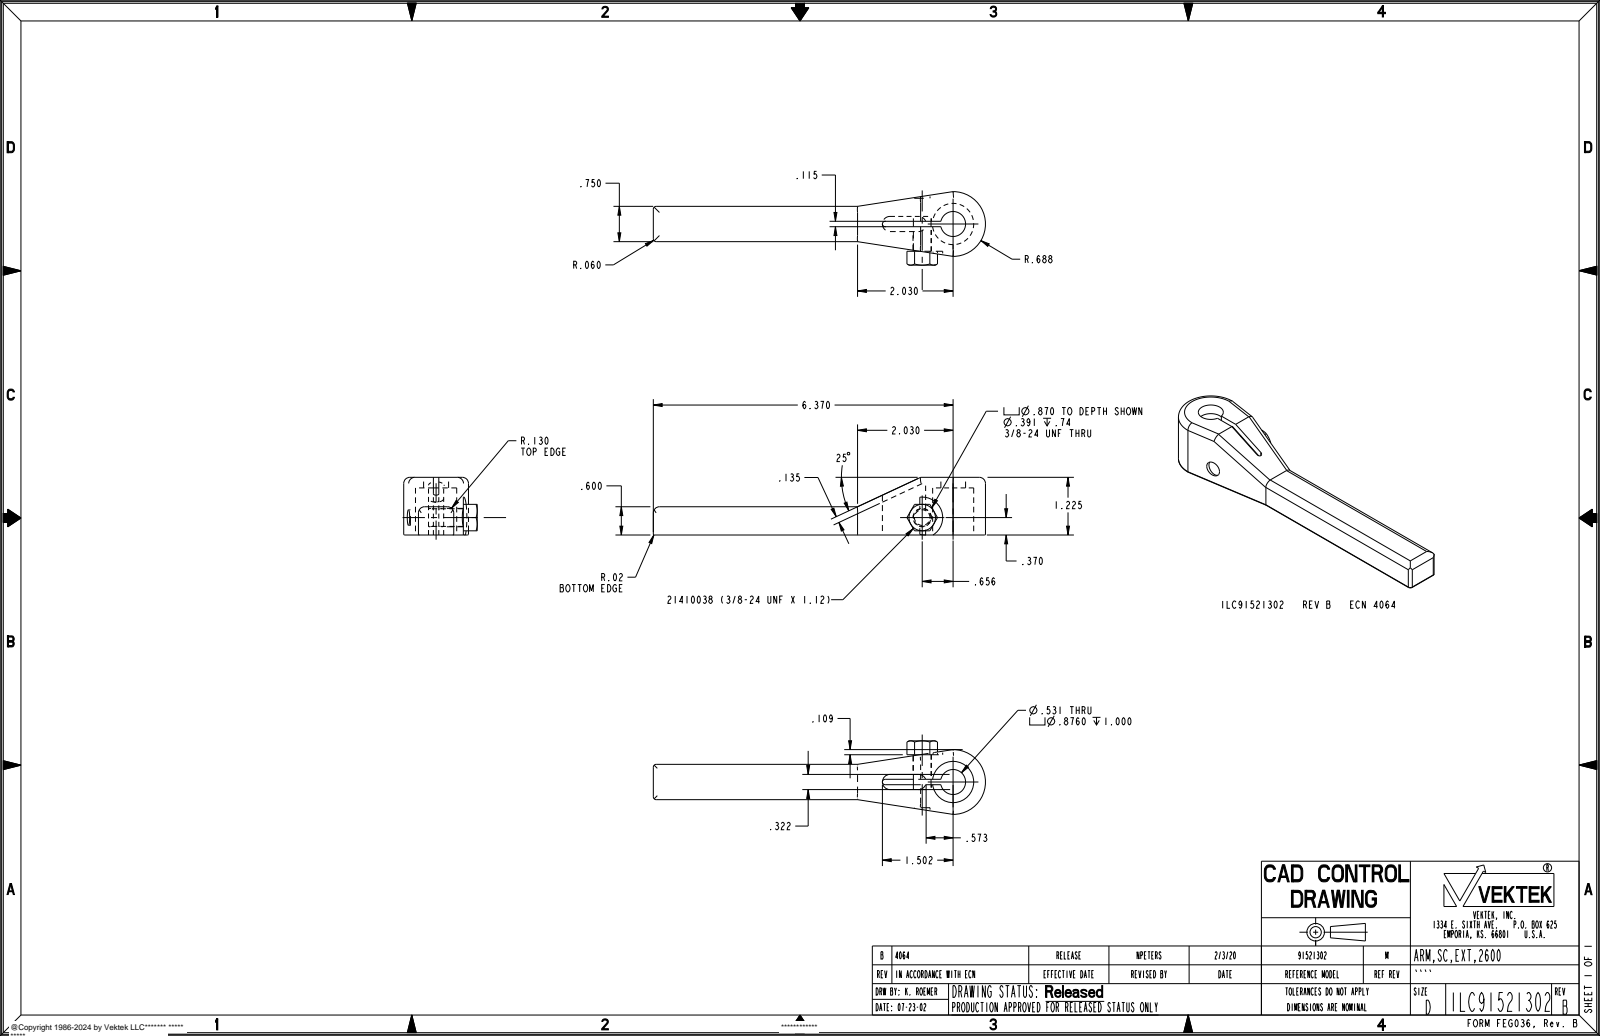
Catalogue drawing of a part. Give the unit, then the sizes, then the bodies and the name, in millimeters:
Units: millimetres
Overall size (bounding box): 179.3 × 39.7 × 31.1
Round holes (diameter × count): ⌀8.4 ×1, ⌀9.9 ×1, ⌀13.5 ×1, ⌀22.3 ×1
Round bosses / shafts (diameter × count): ⌀9.5 ×1
Partial cylindrical surfaces — rounded edges, fillets, slot ends (radius × count): R3.3 ×7, R0.5 ×5, R1.5 ×2, R4.1 ×2, R1.4 ×1, R11 ×1, R17.5 ×1
Main face-to-face distances: 15.2, 19.1, 5.4, 13.6, 31.1, 15.9, 8.1, 11, 2.6, 5.6
Volume: 69 170 mm³ · Surface area: 19 880 mm²
Bodies: 1 solid, 68 faces (26 planar, 32 cylindrical, 10 other)
Part name (STEP PRODUCT): ILC91521302
STEP written by: PRO/ENGINEER BY PARAMETRIC TECHNOLOGY CORPORATION, 2013320 (AUTOMOTIVE_DESIGN)
